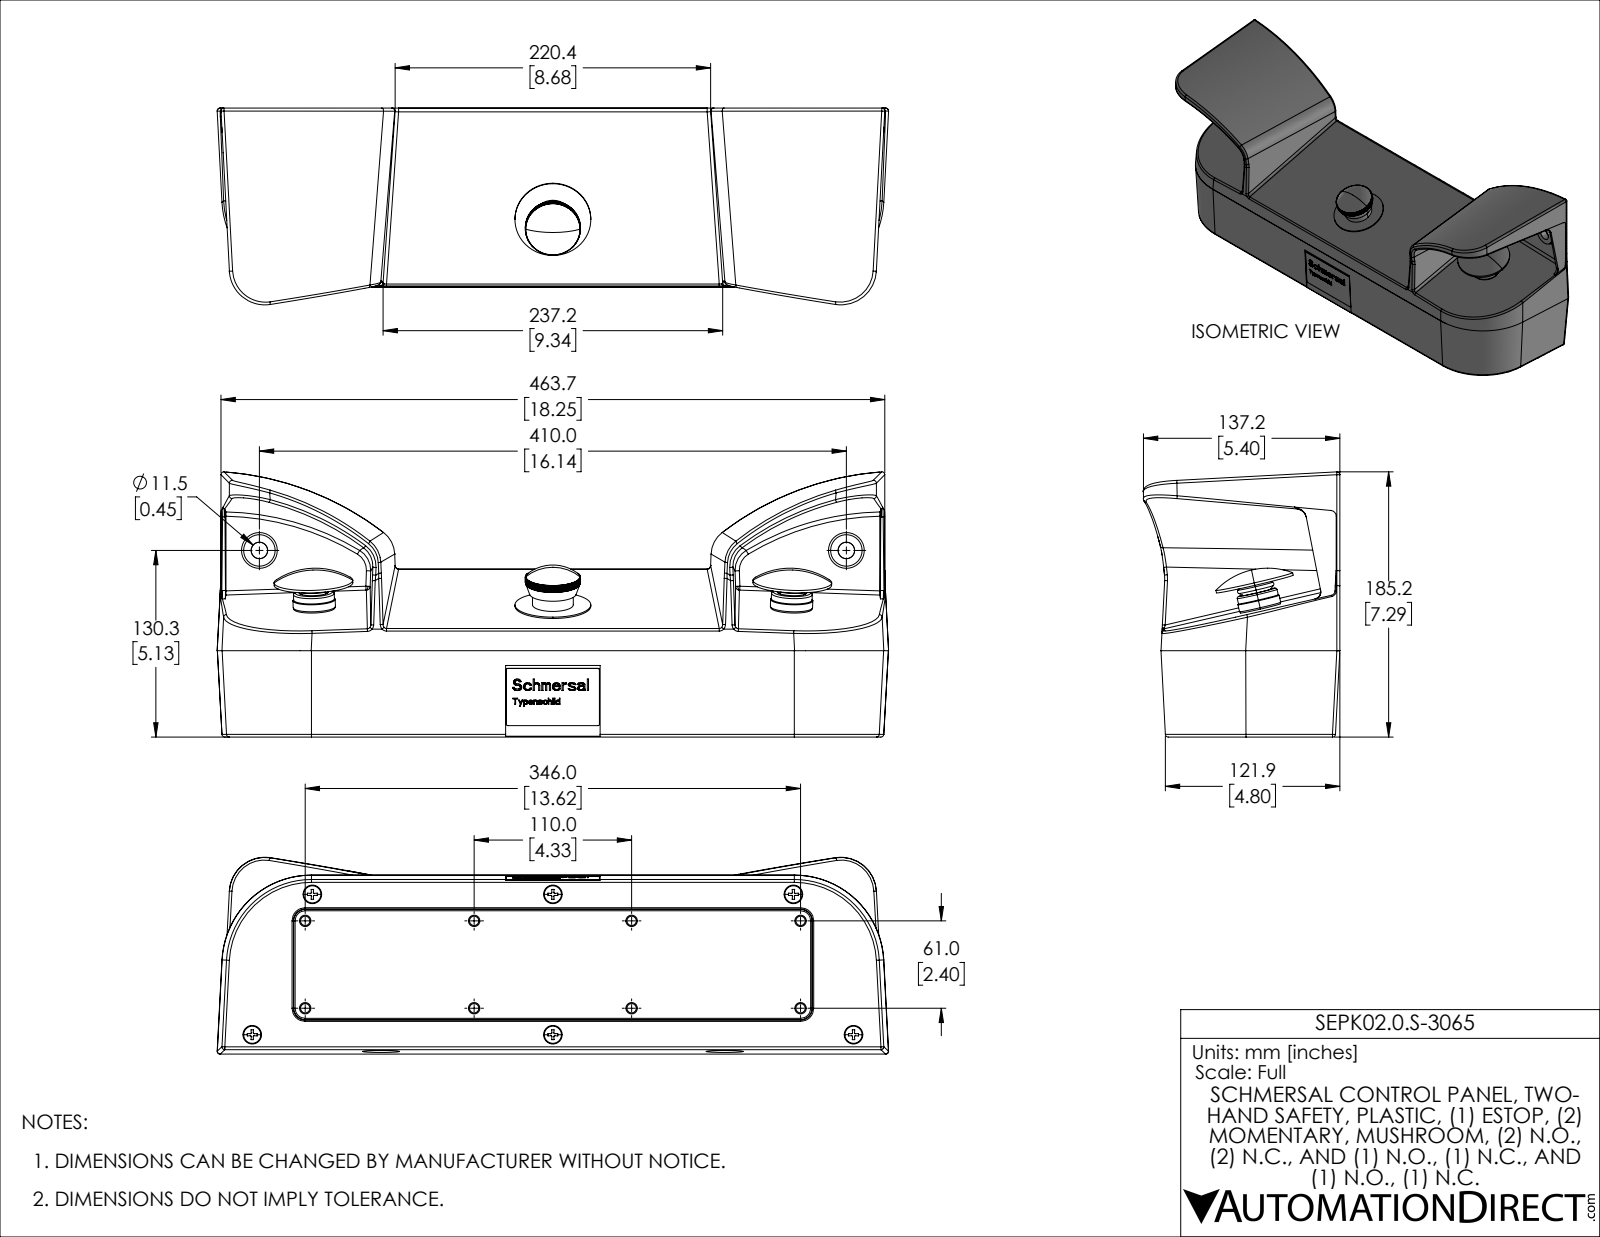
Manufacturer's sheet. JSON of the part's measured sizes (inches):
{"part_name": "SEPK02.0.S-3065", "step_written_by": "SolidWorks 2019 (AUTOMOTIVE_DESIGN)", "units": "inches", "bodies": {"solids": 17, "faces": 2372, "planar": 1491, "cylindrical": 397, "other": 484}, "overall_size": [18.464, 7.291, 5.41], "volume_in3": 77.9, "surface_area_in2": 1084, "round_holes": [[0.256, 14], [0.315, 14], [0.394, 6], [0.512, 6], [0.551, 6], [0.35, 3], [0.768, 3], [1.02, 3], [0.453, 2], [0.669, 2], [0.74, 2], [0.858, 2]], "round_bosses_or_shafts": [[0.551, 8], [0.472, 6], [0.236, 6], [1.122, 3], [0.669, 3], [0.461, 3], [2.165, 2], [1.161, 2]], "partial_cylinders_radius": [[0.039, 98], [0.02, 18], [0.079, 18], [0.059, 6], [0.335, 3], [0.439, 3], [0.024, 2], [0.098, 2]], "face_to_face_distances": [0.157, 0.177, 0.158, 0.335, 0.02, 0.138, 0.059, 4.756, 0.098, 0.137], "hole_center_spacings": [2.285, 2.402, 3.806, 4.646, 5.23, 6.85, 7.496, 8.976]}
